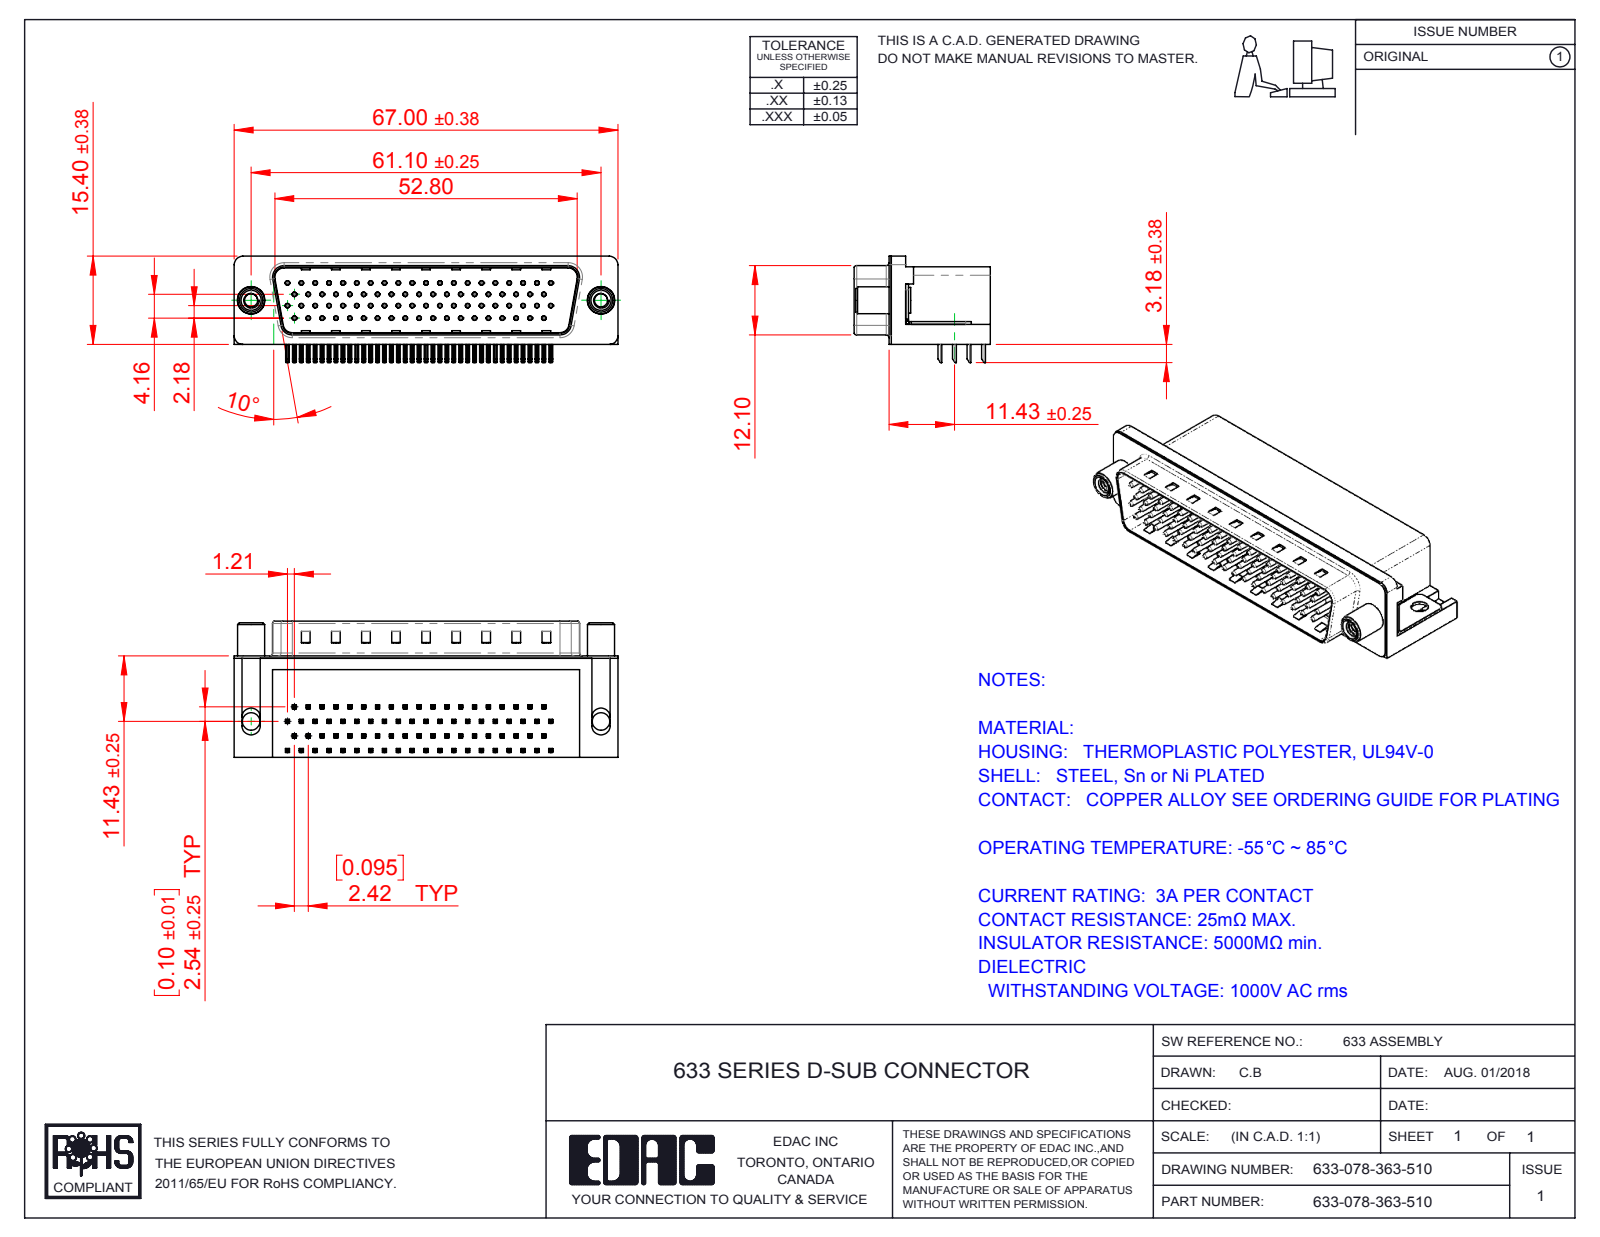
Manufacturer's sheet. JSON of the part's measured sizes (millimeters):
{"part_name": "633 Contact Top_78 Contact; 633-078-363-510; 633 Contact Top 78; 633 Housing_78 Contact (+5 more)", "step_written_by": "SolidWorks 2016 (CONFIG_CONTROL_DESIGN)", "units": "millimeters", "bodies": {"solids": 84, "faces": 6268, "planar": 3971, "cylindrical": 1786, "other": 511}, "overall_size": [67, 23.8, 18.58], "volume_mm3": 14701, "surface_area_mm2": 16535, "round_holes": [[0.35, 78], [0.8, 78], [2.3, 2], [3.05, 2], [3.1, 2], [4, 2], [4.8, 2], [5, 2]], "round_bosses_or_shafts": [[0.75, 78], [4.9, 2], [4.7, 2], [4.5, 2], [3.85, 2]], "partial_cylinders_radius": [[0.25, 312], [0.12, 156], [1, 16], [0.5, 9], [1.6, 8], [1.5, 6], [0.45, 4], [0.9, 4]], "face_to_face_distances": [0.4, 13.2, 17.3, 11.7, 13.35, 2.05, 13.75, 1.65, 1.85, 11.9], "hole_center_spacings": [2.42, 4.84, 7.26, 9.68, 6.26, 7.13, 12.1, 8.62]}
